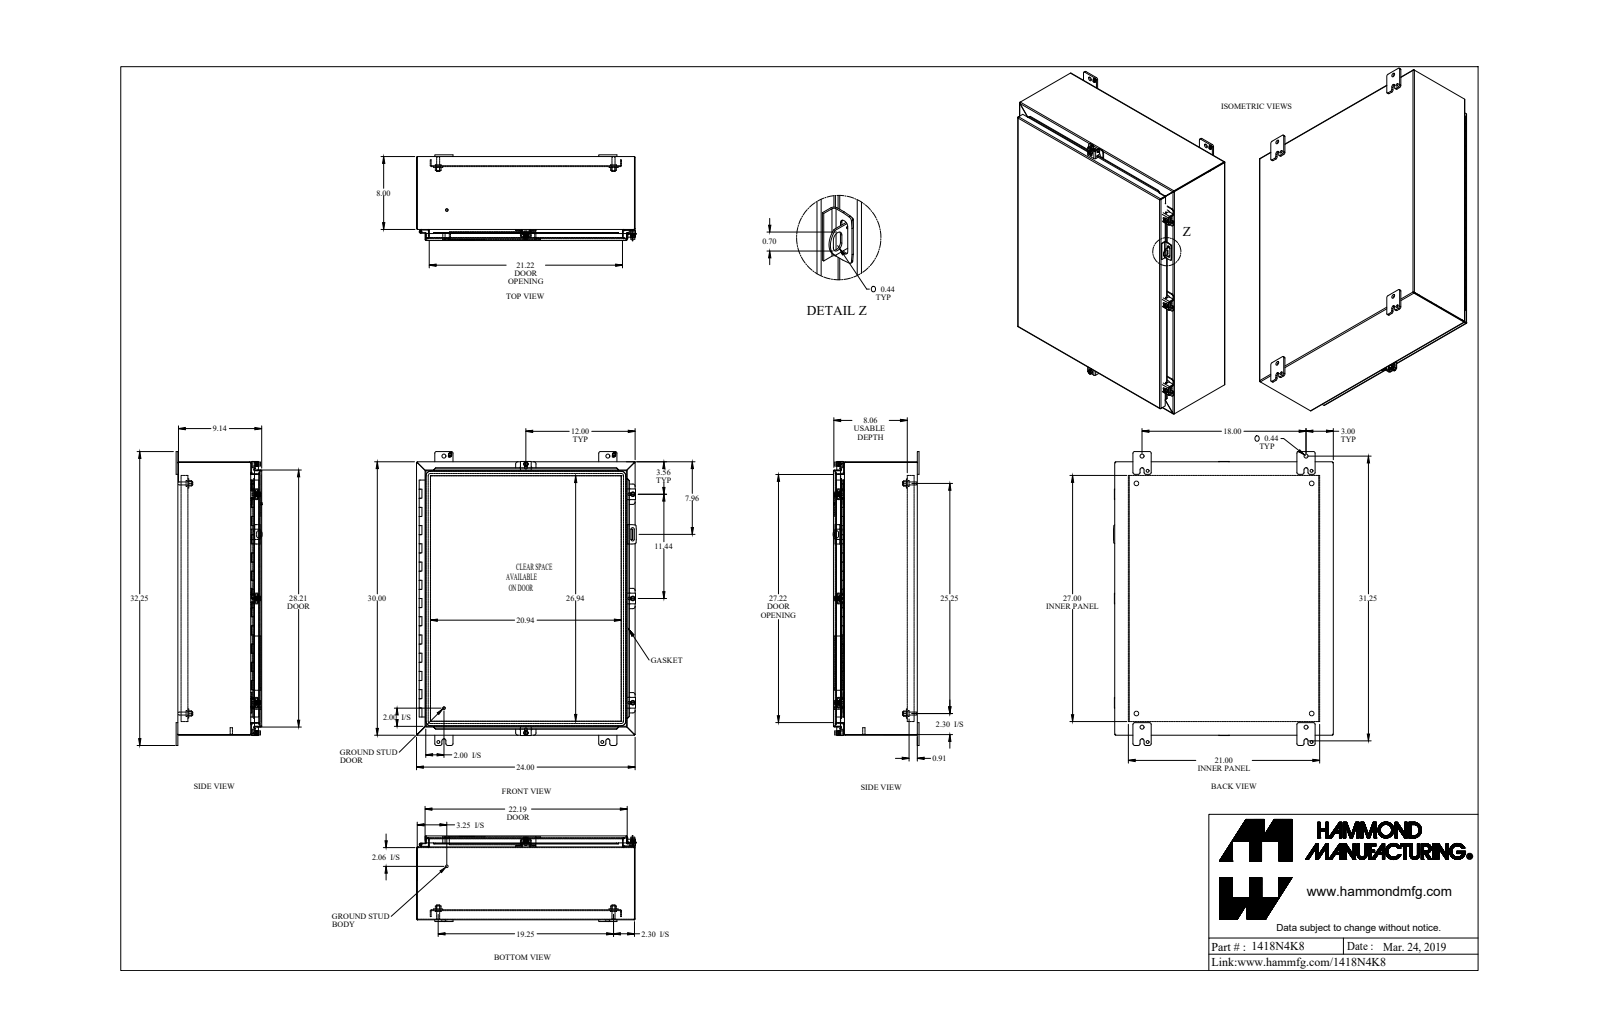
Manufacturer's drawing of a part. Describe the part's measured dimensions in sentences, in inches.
The part is named "1418N4K8_Default". Its 3-D file was written by "SolidWorks 2019 (CONFIG_CONTROL_DESIGN)". It is 43 solids with 1601 faces: 965 planar, 550 cylindrical and 86 other. Overall it measures 32.25 by 24.126 by 9.437 inches. Its volume is 259.4 cubic inches and its surface area 6 777 square inches. Round holes: 5 of diameter 0.213, 5 of diameter 0.265, 5 of diameter 0.375, 4 of diameter 0.313, 4 of diameter 0.437, 4 of diameter 0.5, 2 of diameter 0.307, 2 of diameter 0.445, 1 of diameter 0.125, 1 of diameter 0.187. Round bosses or shafts: 5 of diameter 0.5, 5 of diameter 0.39, 5 of diameter 0.244, 4 of diameter 0.65, 4 of diameter 0.375, 4 of diameter 0.33, 2 of diameter 1, 2 of diameter 0.281. Partial cylindrical surfaces (rounded edges, fillets, slot ends): 27 of radius 0.048, 27 of radius 0.143, 26 of radius 0.188, 24 of radius 0.036, 24 of radius 0.108, 24 of radius 0.25, 10 of radius 0.125, 10 of radius 0.141. The main face-to-face distances are 0.072, 0.072, 9.066, 9.138, 9.138, 9.21, 0.095, 8.106, 8.034, 1.032. The hole center spacings are 29.018, 1.736, 9.857, 18, 29.75, 34.772, 2.434, 3.065.
